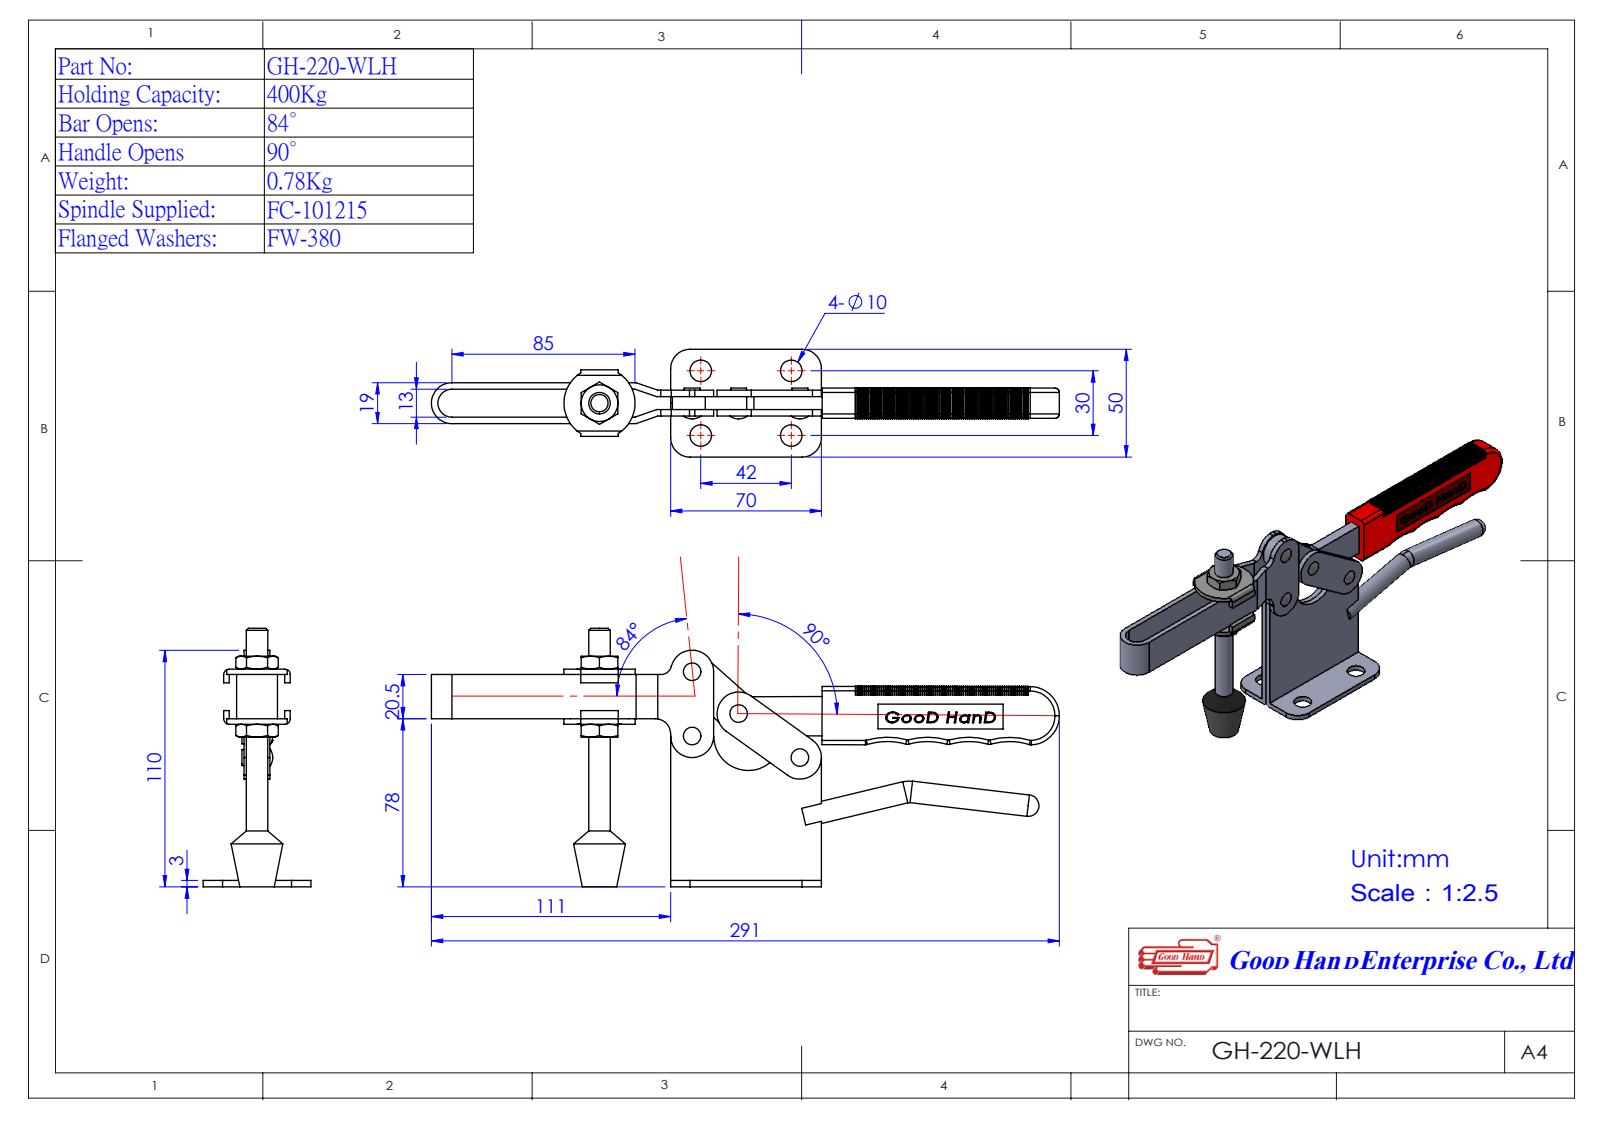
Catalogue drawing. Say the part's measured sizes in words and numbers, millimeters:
The part is named "1200W01; GH-200-W 6.35-12; GH-220-WLH; 1200W05 (+8 more)". Its 3-D file was written by "SolidWorks 2016 (AUTOMOTIVE_DESIGN)". It is 18 solids with 1448 faces: 841 planar, 473 cylindrical and 134 other. Overall it measures 291.4 by 120 by 50 millimeters. Its volume is 135 876 cubic millimeters and its surface area 85 109 square millimeters. Round holes: 5 of diameter 10, 3 of diameter 6.33, 2 of diameter 6.3, 2 of diameter 6.35, 1 of diameter 4.6, 1 of diameter 5, 1 of diameter 8.5, 1 of diameter 9.3. Round bosses or shafts: 4 of diameter 7.35, 2 of diameter 10, 2 of diameter 6.35, 1 of diameter 20. Partial cylindrical surfaces (rounded edges, fillets, slot ends): 11 of radius 2, 6 of radius 2.2, 5 of radius 3, 5 of radius 9, 4 of radius 2.54, 4 of radius 32, 3 of radius 10, 2 of radius 5. The main face-to-face distances are 3, 6, 6.5, 3.5, 9.5, 12.5, 0.5, 13, 4, 7. The hole center spacings are 30, 42, 49.34, 51.61, 73.65, 90.26, 97.46, 0.37.
